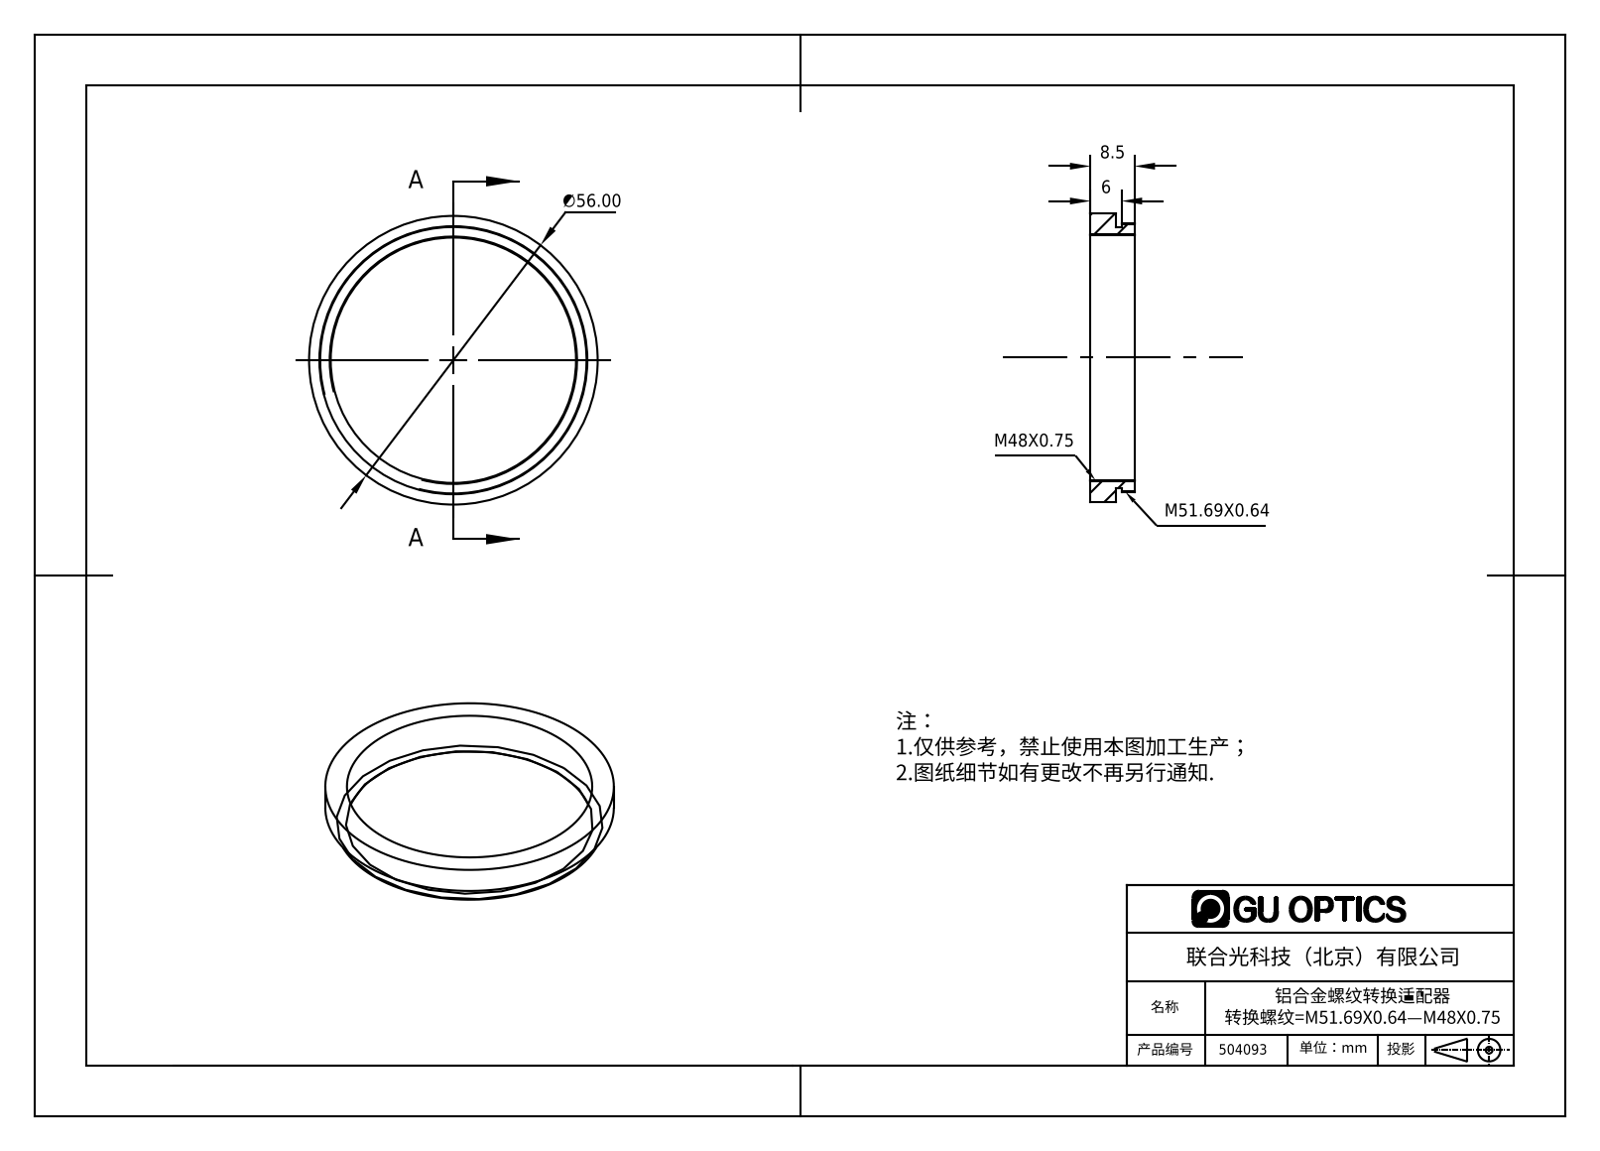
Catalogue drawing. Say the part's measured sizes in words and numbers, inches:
The part is named "504093". Its 3-D file was written by "SolidWorks 2016 (AUTOMOTIVE_DESIGN)". It is 1 solid with 12 faces: 4 planar, 8 cylindrical and 0 other. Overall it measures 2.205 by 2.205 by 0.335 inches. Its volume is 0.276 cubic inches and its surface area 6.632 square inches. Round holes: 1 of diameter 1.874. Round bosses or shafts: 1 of diameter 2.205, 1 of diameter 2.047, 1 of diameter 2. The main face-to-face distances are 0.197, 0.138, 0.335, 0.098, 0.039, 0.236.
